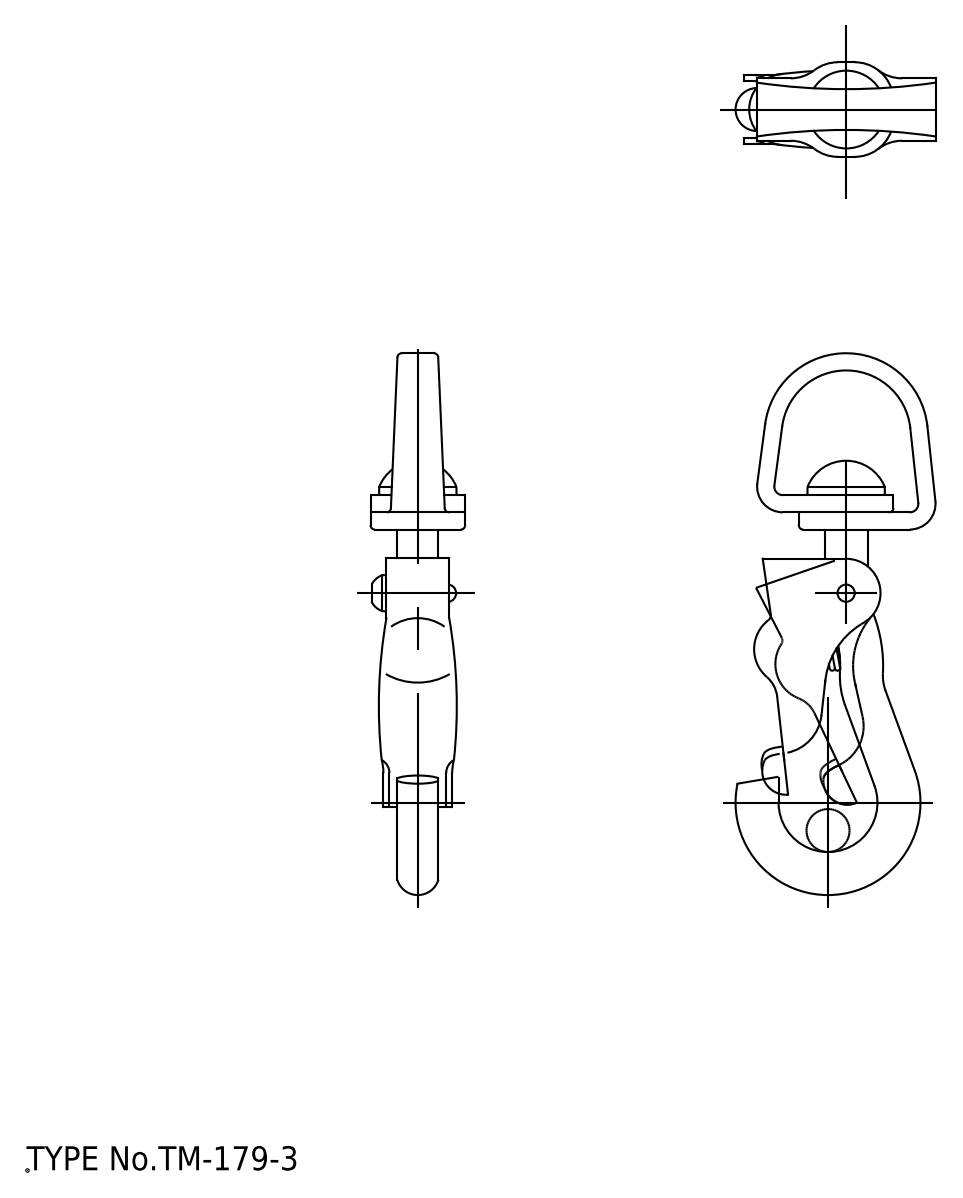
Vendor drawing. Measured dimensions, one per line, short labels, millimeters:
name: Dカン; フック; レバー
written by: spGate 20.6.3 (****-****-****-****) (AUTOMOTIVE_DESIGN)
unit: mm
bodies: 3 solids, 201 faces (48 planar, 85 cylindrical, 68 other)
size: 63 × 23.23 × 11
volume: 2 812 mm³; area: 3 696 mm²
holes: 1× ⌀2, 1× ⌀7
rounds: 14× R2, 8× R4.5, 7× R0.7, 4× R3, 2× R0.5, 2× R1, 2× R1.2, 2× R1.7
face distances: 0.7, 0.55, 5.35, 6.6, 6.05, 1.25, 2, 4, 7.3, 5.9
